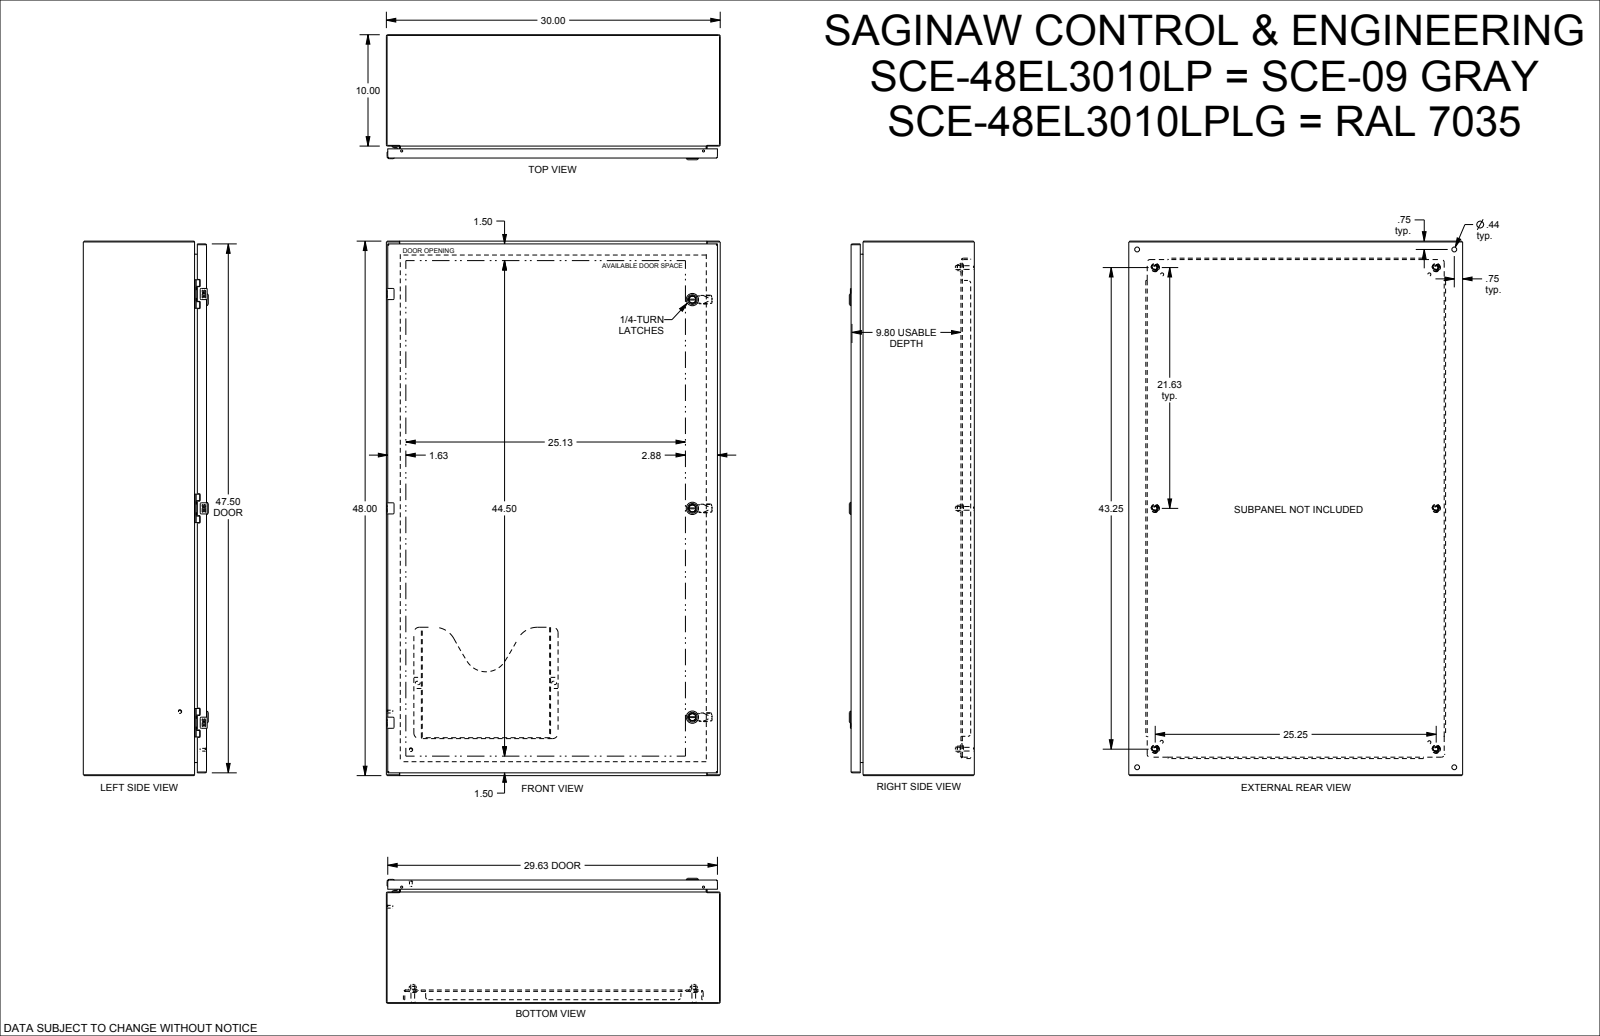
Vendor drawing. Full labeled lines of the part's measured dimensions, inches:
Part name (STEP PRODUCT): SCE-48EL3010LP
STEP written by: SolidWorks 2019 (CONFIG_CONTROL_DESIGN)
Units: inches
Bodies: 0 solids, 3818 faces (1807 planar, 1058 cylindrical, 953 other)
Overall size (bounding box): 48 × 30 × 11.23
Round holes (diameter × count): ⌀0.172 ×6, ⌀0.205 ×6, ⌀0.244 ×6, ⌀0.266 ×6, ⌀0.367 ×6, ⌀0.375 ×6, ⌀0.5 ×6, ⌀0.281 ×4, ⌀0.437 ×4, ⌀0.04 ×3, ⌀0.156 ×3, ⌀0.197 ×3
Round bosses / shafts (diameter × count): ⌀0.17 ×9, ⌀0.366 ×6, ⌀0.332 ×6, ⌀0.25 ×6, ⌀0.24 ×6, ⌀0.248 ×4, ⌀0.196 ×4, ⌀1.102 ×3
Partial cylindrical surfaces — rounded edges, fillets, slot ends (radius × count): R0.012 ×82, R0.01 ×40, R0.015 ×32, R0.02 ×28, R0.04 ×17, R0.025 ×16, R0.1 ×16, R0.03 ×15
Main face-to-face distances: 0.075, 0.075, 10.923, 10.998, 11.073, 10.998, 1.2, 9.873, 0.125, 1
Hole centre spacings: 19.25, 0.985, 38.5, 0.02, 0.493, 0.494, 4.493, 18.265
